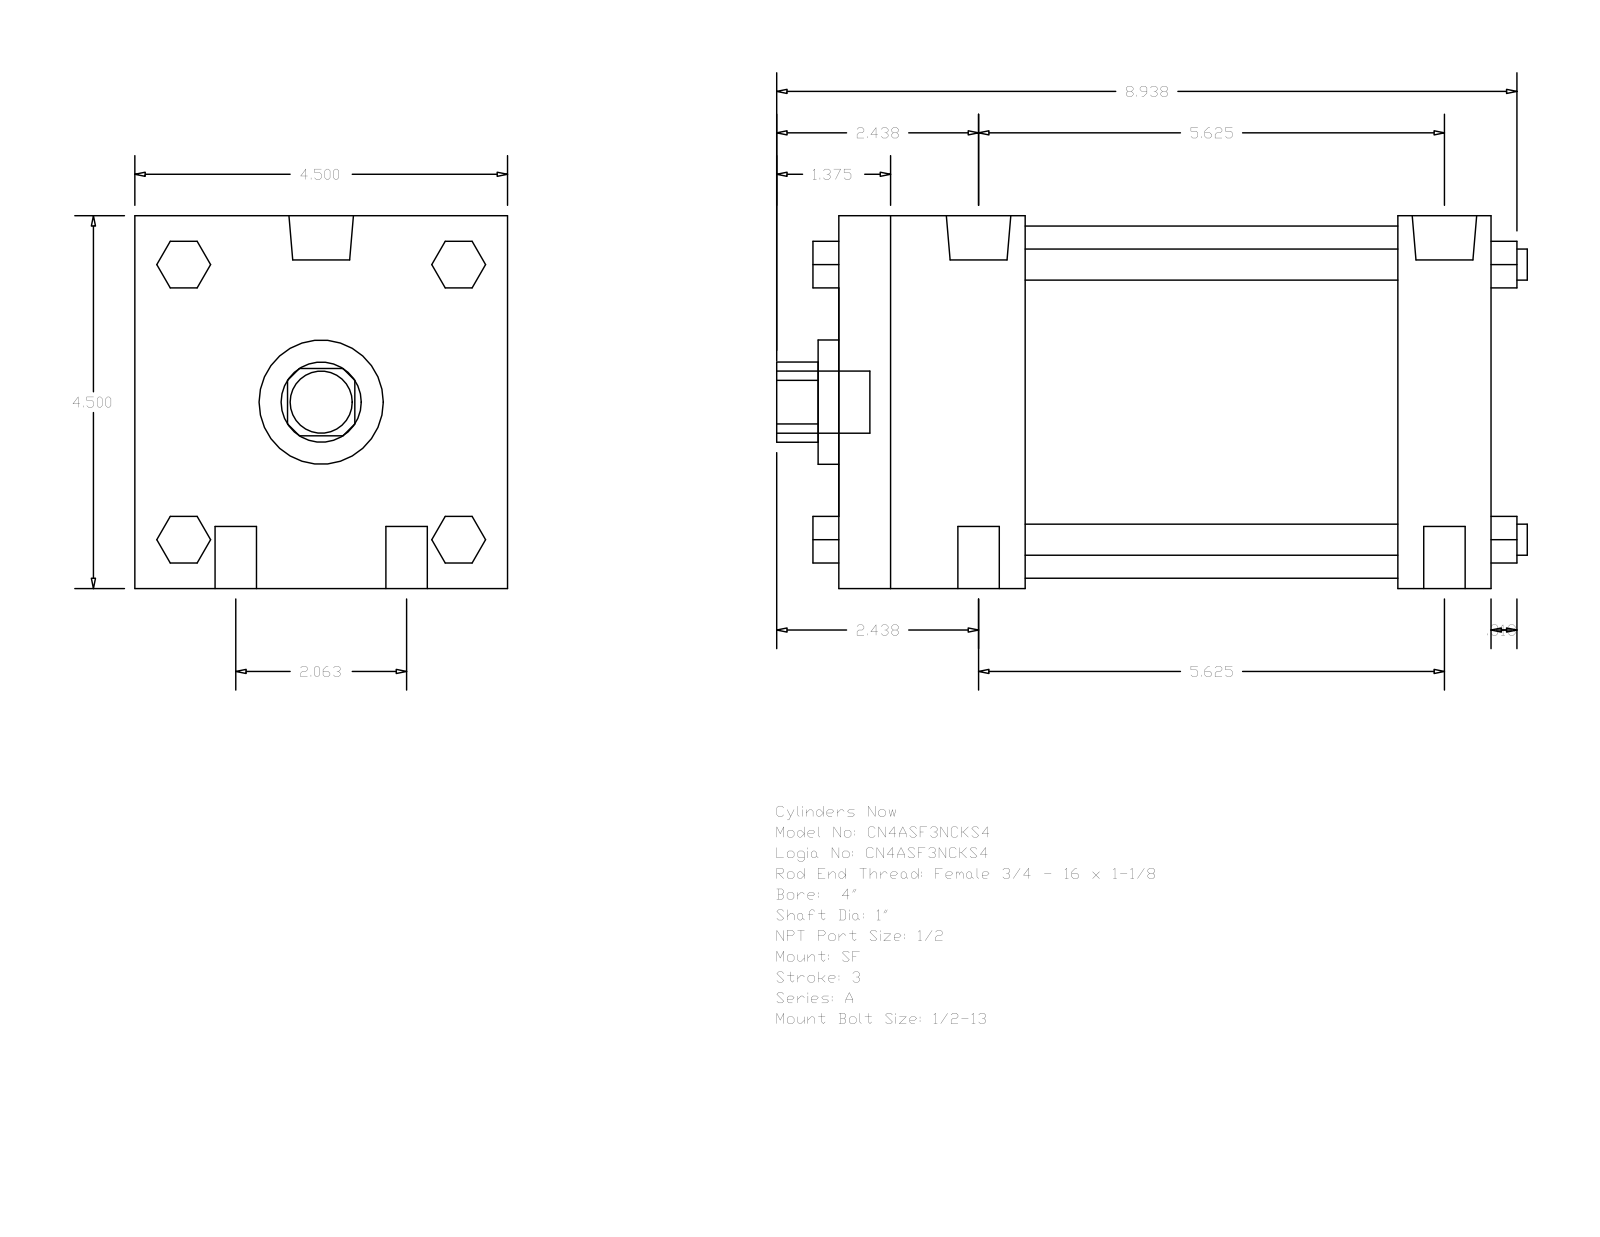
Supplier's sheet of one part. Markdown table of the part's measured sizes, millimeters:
| quantity | value |
| --- | --- |
| part name | A_SF__0400_1 |
| STEP written by | GSSL Pune (CONFIG_CONTROL_DESIGN) |
| units | millimeters |
| bodies | 0 solids, 124 faces (94 planar, 30 cylindrical, 0 other) |
| overall size | 230.19 × 114.3 × 114.3 |
| round holes (diameter × count) | 25.4 × 1, 38.1 × 1, 107.95 × 1 |
| round bosses / shafts (diameter × count) | 12.7 × 4, 9.53 × 4, 19.77 × 2, 8.73 × 2, 19.05 × 1 |
| partial cylindrical surfaces (radius × count) | 12.29 × 1 |
| main face-to-face distances | 114.3, 200.02, 28.57, 171.45, 57.15, 142.87, 14.29, 42.16, 73.03, 7.94 |
